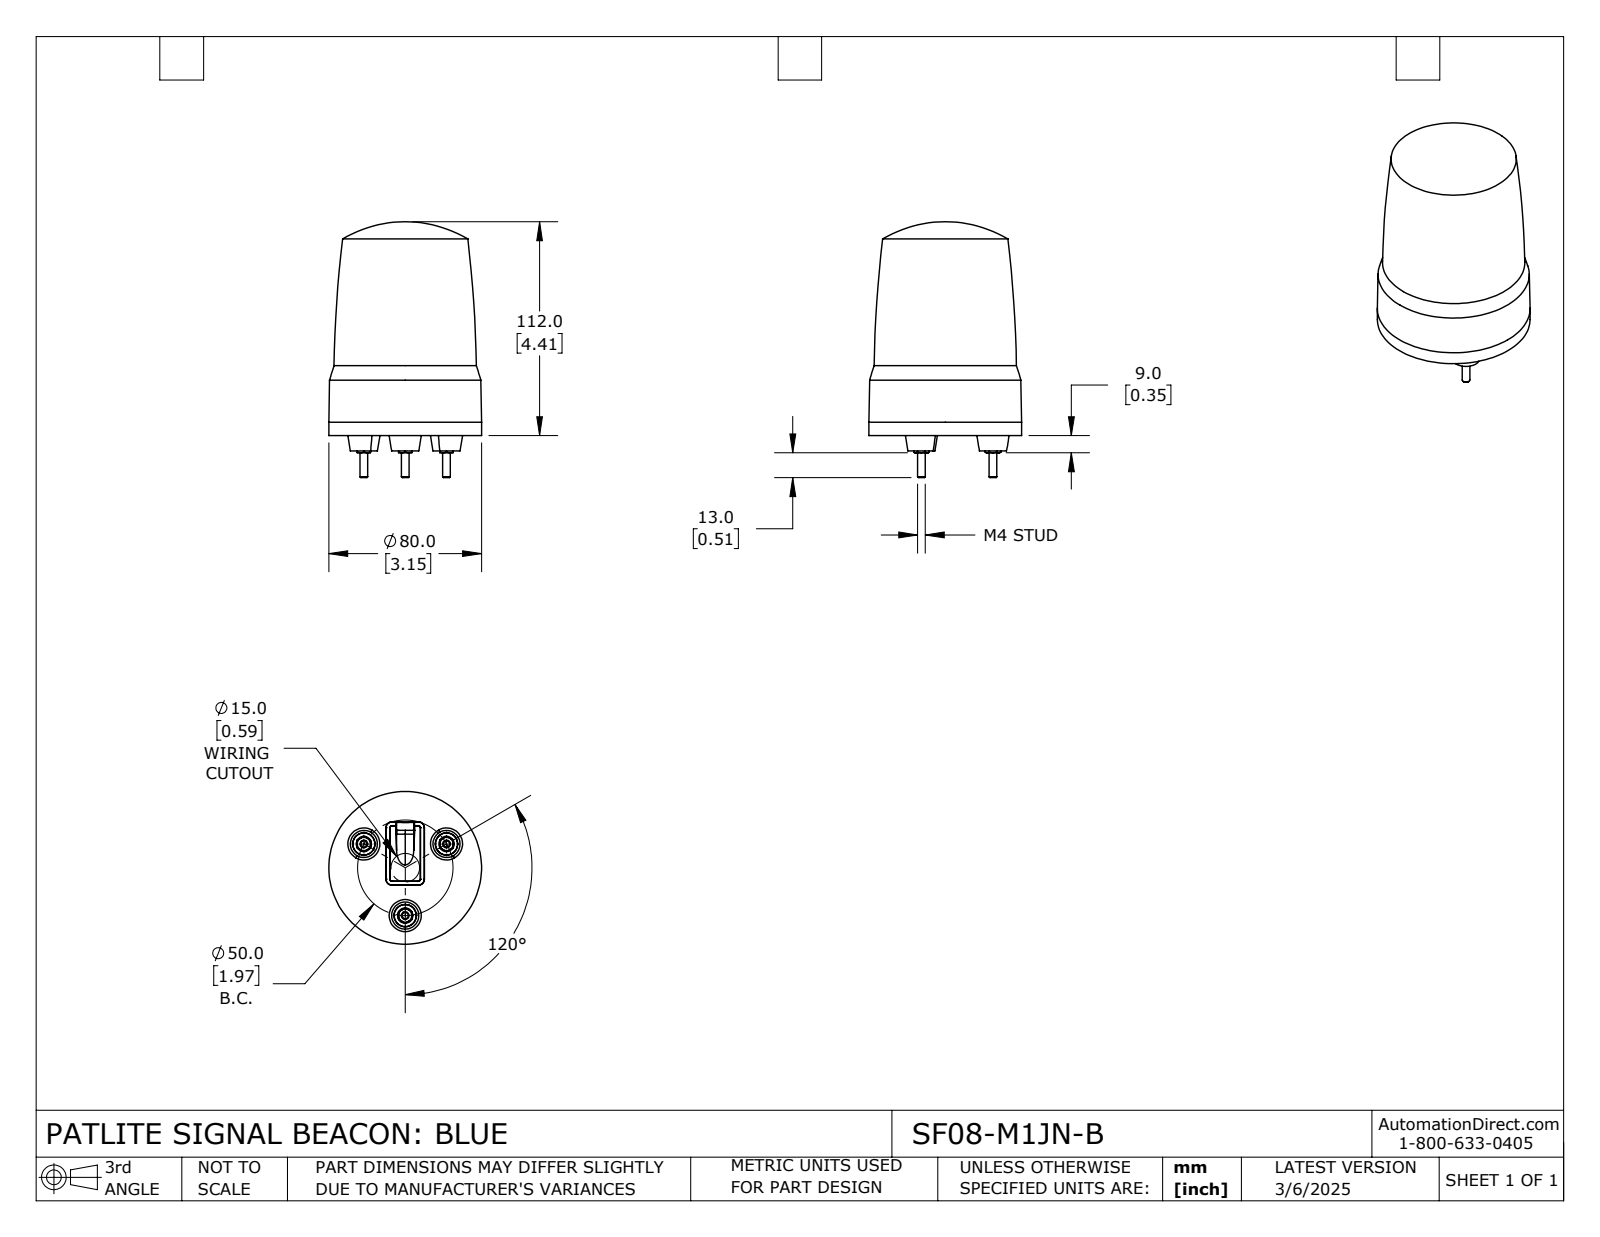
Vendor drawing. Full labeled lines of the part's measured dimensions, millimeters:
Part name (STEP PRODUCT): SF08-M1JN-B
STEP written by: SolidWorks 2024 (CONFIG_CONTROL_DESIGN)
Units: millimetres
Bodies: 1 solid, 138 faces (47 planar, 14 cylindrical, 77 other)
Overall size (bounding box): 134 × 80 × 80
Volume: 463 225 mm³ · Surface area: 35 408 mm²
Round bosses / shafts (diameter × count): ⌀8 ×3, ⌀4 ×3, ⌀80 ×1
Main face-to-face distances: 0.85, 2.45, 1.6, 5.3, 6.15, 7.75, 2.7, 8, 8.85, 10.45
